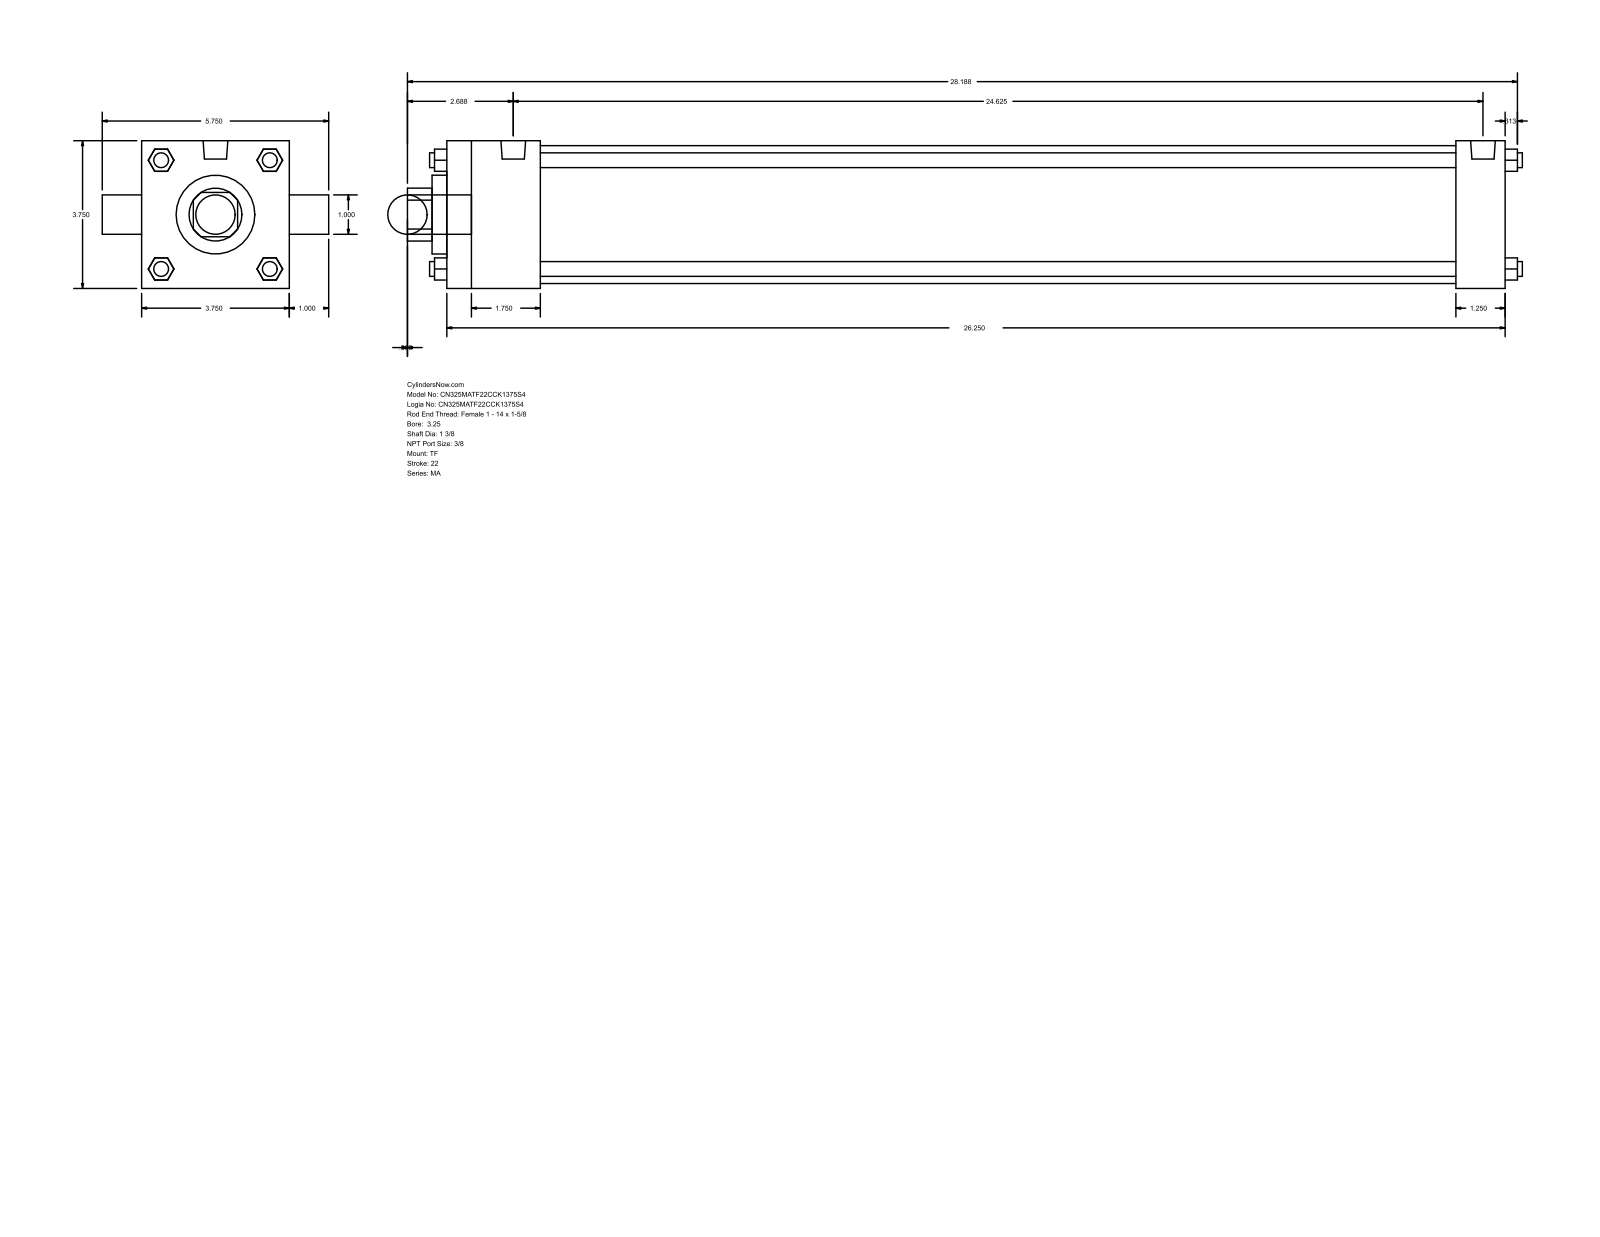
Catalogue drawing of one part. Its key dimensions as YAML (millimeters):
part_name: "MA_TF__0325_1.375"
step_written_by: "GSSL Pune (CONFIG_CONTROL_DESIGN)"
units: millimeters
bodies: {solids: 0, faces: 120, planar: 92, cylindrical: 28, other: 0}
overall_size: [719.14, 146.05, 95.25]
round_holes:
  - {diameter: 25.4, count: 1}
  - {diameter: 34.92, count: 1}
  - {diameter: 50.8, count: 1}
  - {diameter: 88.9, count: 1}
round_bosses_or_shafts:
  - {diameter: 9.53, count: 4}
  - {diameter: 11.11, count: 3}
  - {diameter: 15.93, count: 2}
  - {diameter: 25.4, count: 1}
partial_cylinders:
  - {radius: 17.06, count: 1}
face_to_face_distances: [95.24, 682.62, 60.32, 650.87, 590.55, 622.3, 31.75, 9.52, 69.84, 660.39]
